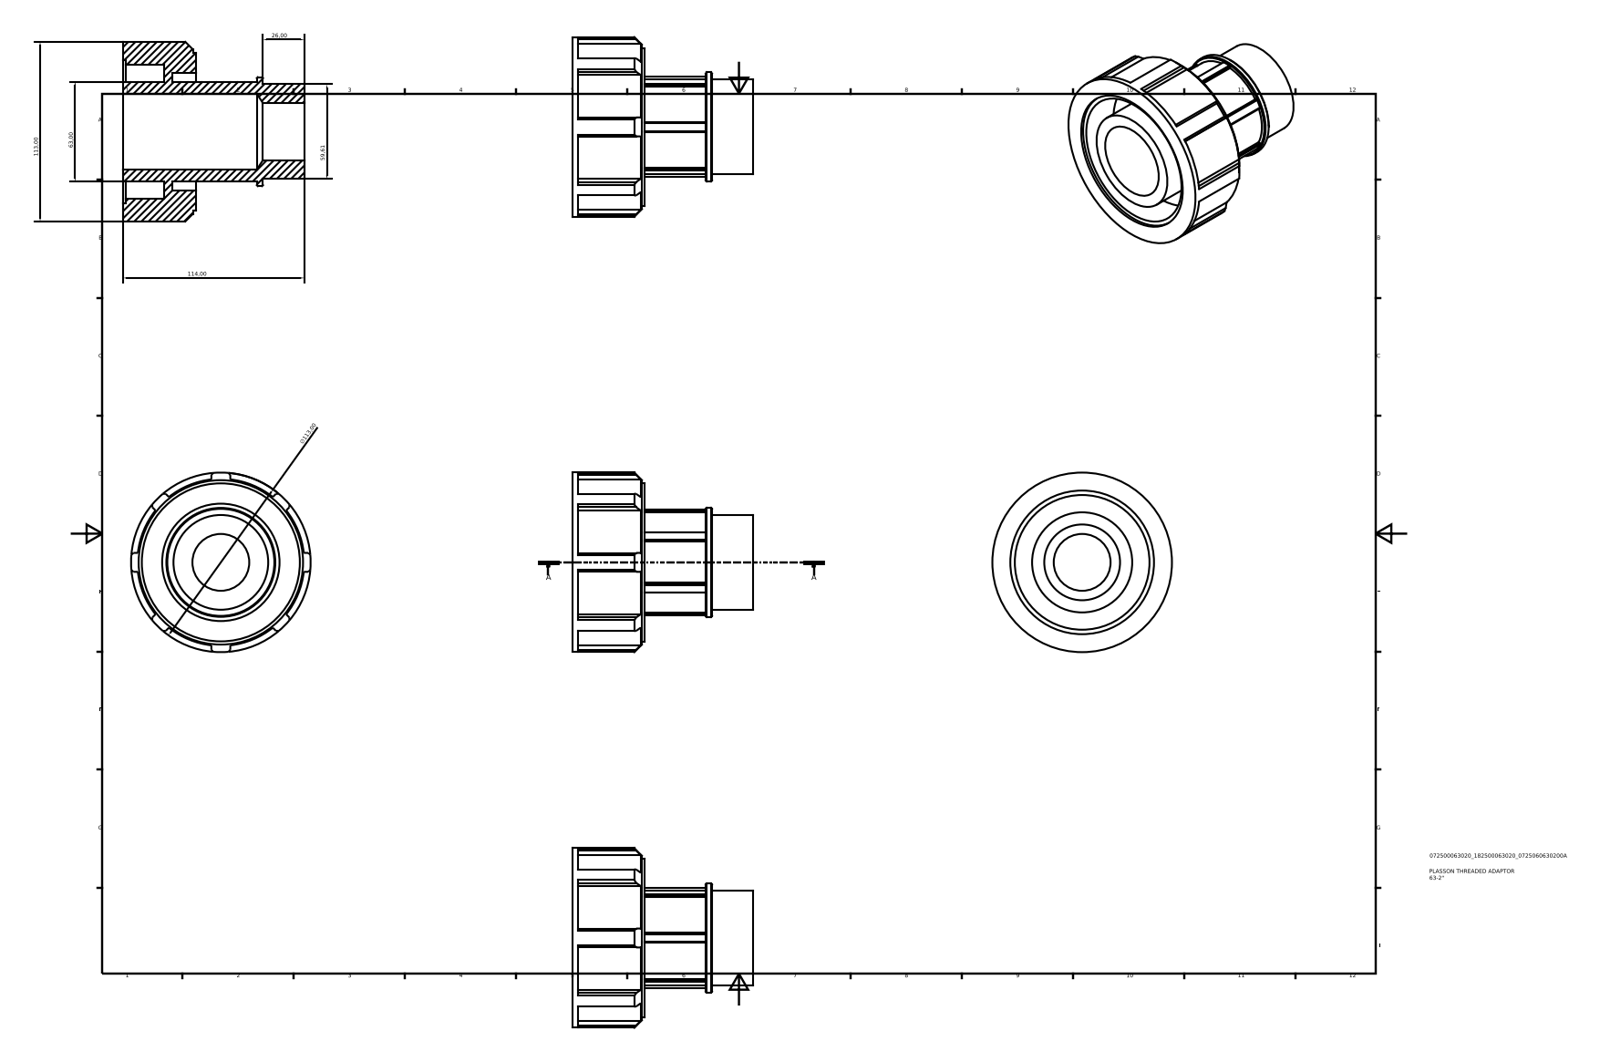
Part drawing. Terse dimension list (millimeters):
name: 072500063020_182500063020
written by: Autodesk Inventor 2015 (AUTOMOTIVE_DESIGN)
unit: mm
bodies: 1 solid, 108 faces (74 planar, 30 cylindrical, 4 other)
size: 114 × 113 × 113
volume: 356 766 mm³; area: 83 803 mm²
holes: 1× ⌀35.77, 1× ⌀47.69, 1× ⌀73.88, 1× ⌀84.75, 1× ⌀90.4
bosses: 1× ⌀113, 1× ⌀99.44, 1× ⌀68.56, 1× ⌀63, 1× ⌀59.61
rounds: 1× R33.08, 1× R52.55
face distances: 45.6, 26, 88, 19.6, 1.71, 114, 68.4, 42.18, 43.89, 31.2
